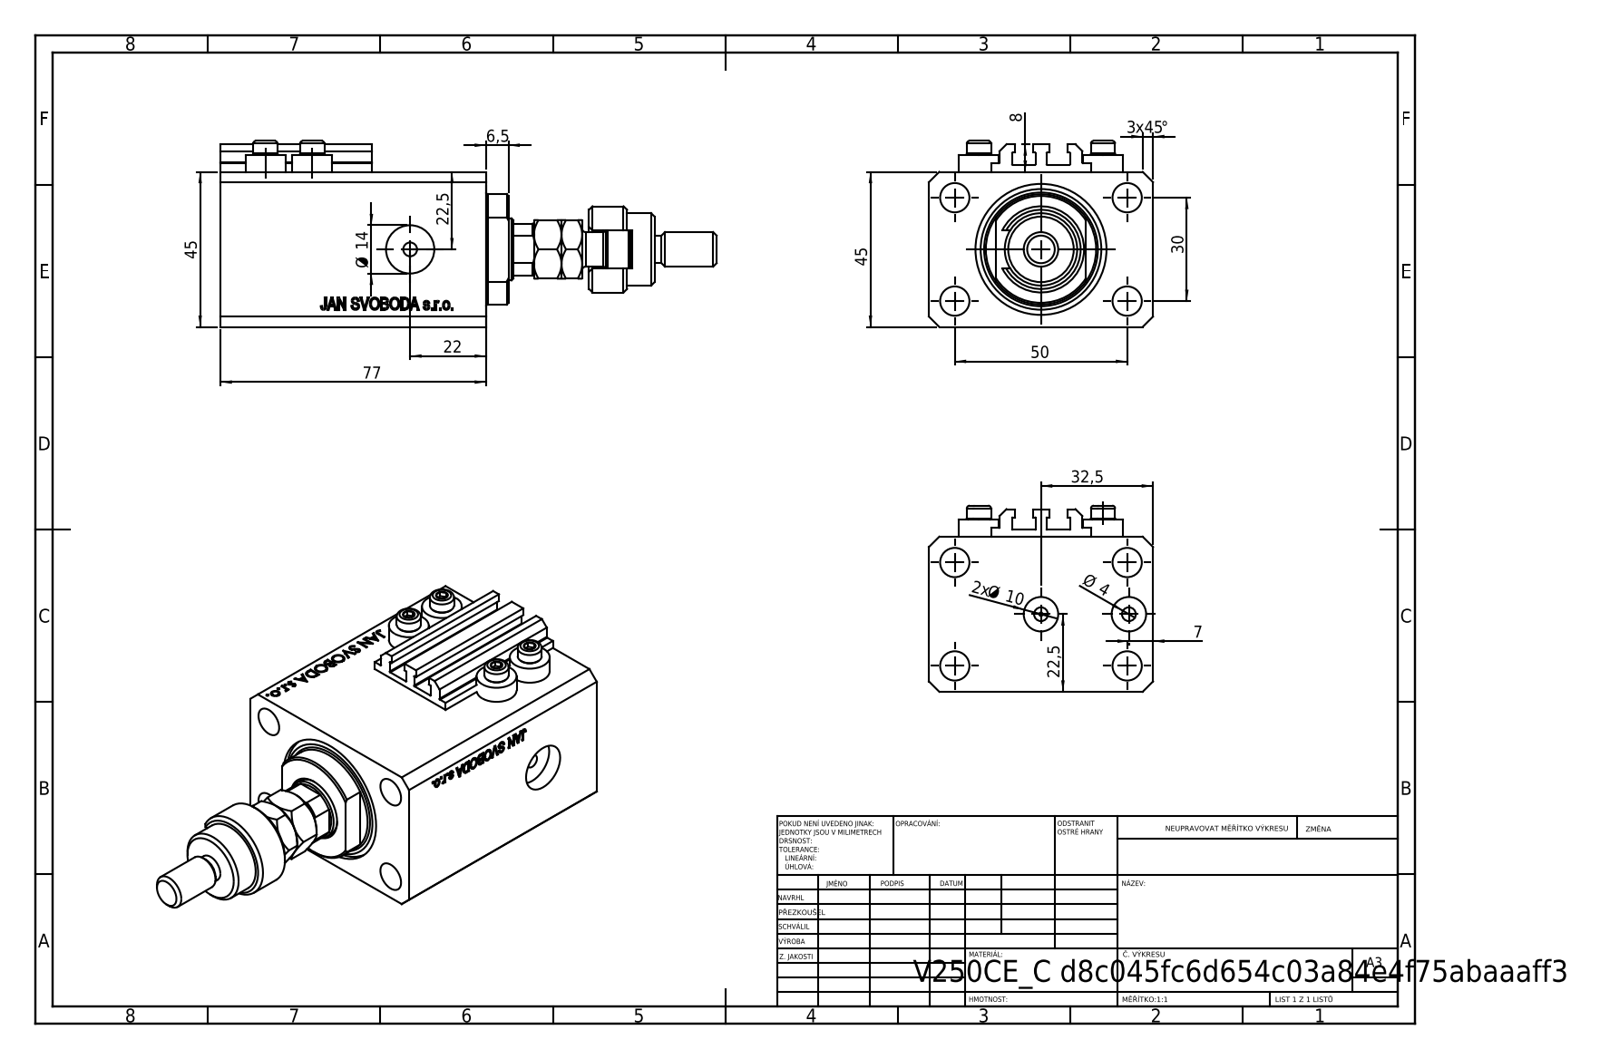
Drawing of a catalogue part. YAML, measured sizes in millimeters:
part_name: "V250CE_VC_C; MFA; ALLEN BOLT V250CE; FEMALE_PART_FOR_DFA (+2 more)"
step_written_by: "SolidWorks 2019 (CONFIG_CONTROL_DESIGN)"
units: millimeters
bodies: {solids: 10, faces: 1127, planar: 532, cylindrical: 105, other: 490}
overall_size: [143.9, 65, 54]
volume: 223352
surface_area: 65200
round_holes:
  - {diameter: 4, count: 8}
  - {diameter: 8.5, count: 5}
  - {diameter: 14, count: 2}
  - {diameter: 1.25, count: 1}
  - {diameter: 10, count: 1}
  - {diameter: 18, count: 1}
  - {diameter: 38, count: 1}
round_bosses_or_shafts:
  - {diameter: 11.6, count: 4}
  - {diameter: 7, count: 4}
  - {diameter: 25, count: 1}
  - {diameter: 21, count: 1}
  - {diameter: 16, count: 1}
  - {diameter: 10, count: 1}
  - {diameter: 8, count: 1}
partial_cylinders:
  - {radius: 0.2, count: 10}
  - {radius: 5.5, count: 1}
  - {radius: 8.5, count: 1}
  - {radius: 8.75, count: 1}
  - {radius: 16, count: 1}
face_to_face_distances: [45, 65, 77, 51.9, 25.1, 3, 6.9, 70.1, 14, 5]
hole_center_spacings: [29.15, 13.6, 15.01, 30, 36, 38.48, 50, 52.68]
